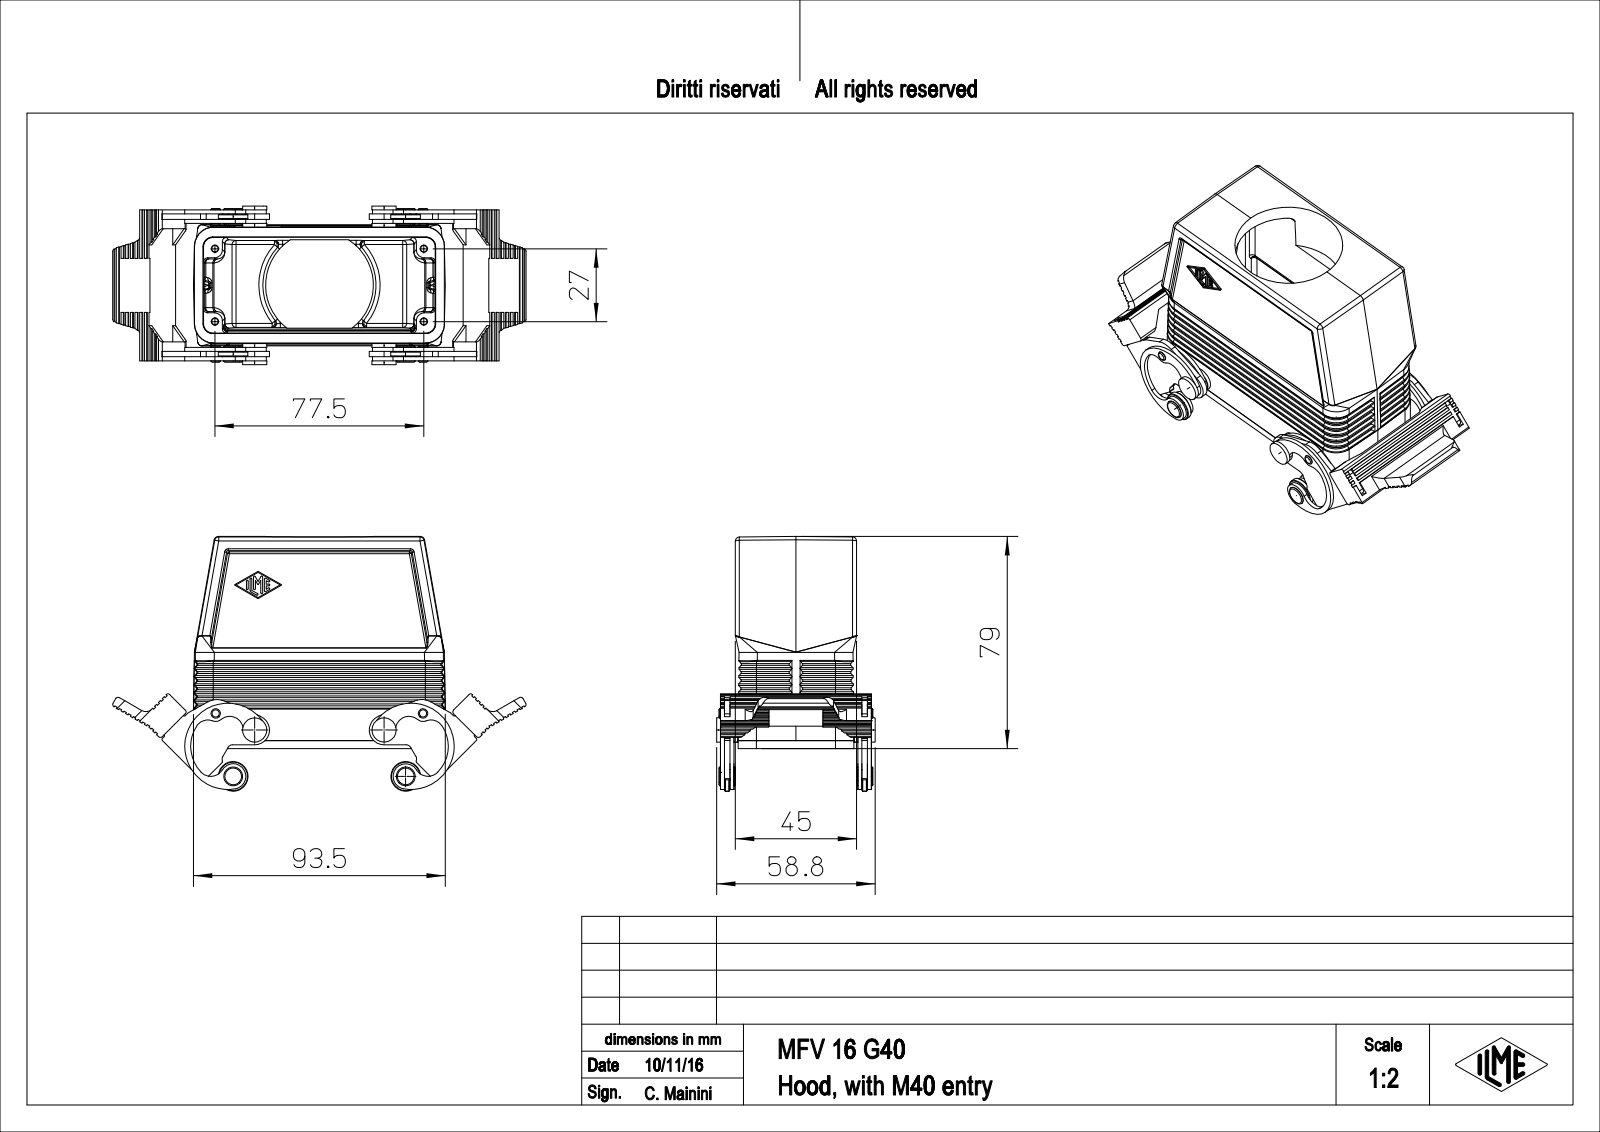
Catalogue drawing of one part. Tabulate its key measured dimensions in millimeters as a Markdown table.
| quantity | value |
| --- | --- |
| part name | MFV_16_G40 |
| STEP written by | PTC Creo Elements/Direct Modeling 19.0E 27-Jun-2016 (C) Parametric Technology GmbH (AUTOMOTIVE_DESIGN) |
| units | millimeters |
| bodies | 1 solid, 1267 faces (675 planar, 408 cylindrical, 184 other) |
| overall size | 153.47 × 94.54 × 58.8 |
| volume | 116 877 mm³ |
| surface area | 64 830 mm² |
| round holes (diameter × count) | 2.75 × 4, 5 × 4, 3.1 × 2, 4 × 2, 40 × 1 |
| round bosses / shafts (diameter × count) | 11 × 2, 9 × 2, 7 × 2, 4.8 × 2, 3.5 × 2, 3 × 2 |
| partial cylindrical surfaces (radius × count) | 0.5 × 86, 1.5 × 16, 3 × 12, 1 × 10, 7 × 10, 5 × 6, 2 × 4, 3.5 × 4 |
| main face-to-face distances | 2, 1, 3.5, 43, 51, 1.5, 4, 7, 52.5, 54.5 |
| hole center spacings | 19, 19.11, 24.25, 27, 34.07, 41.02, 41.03, 74.29 |
